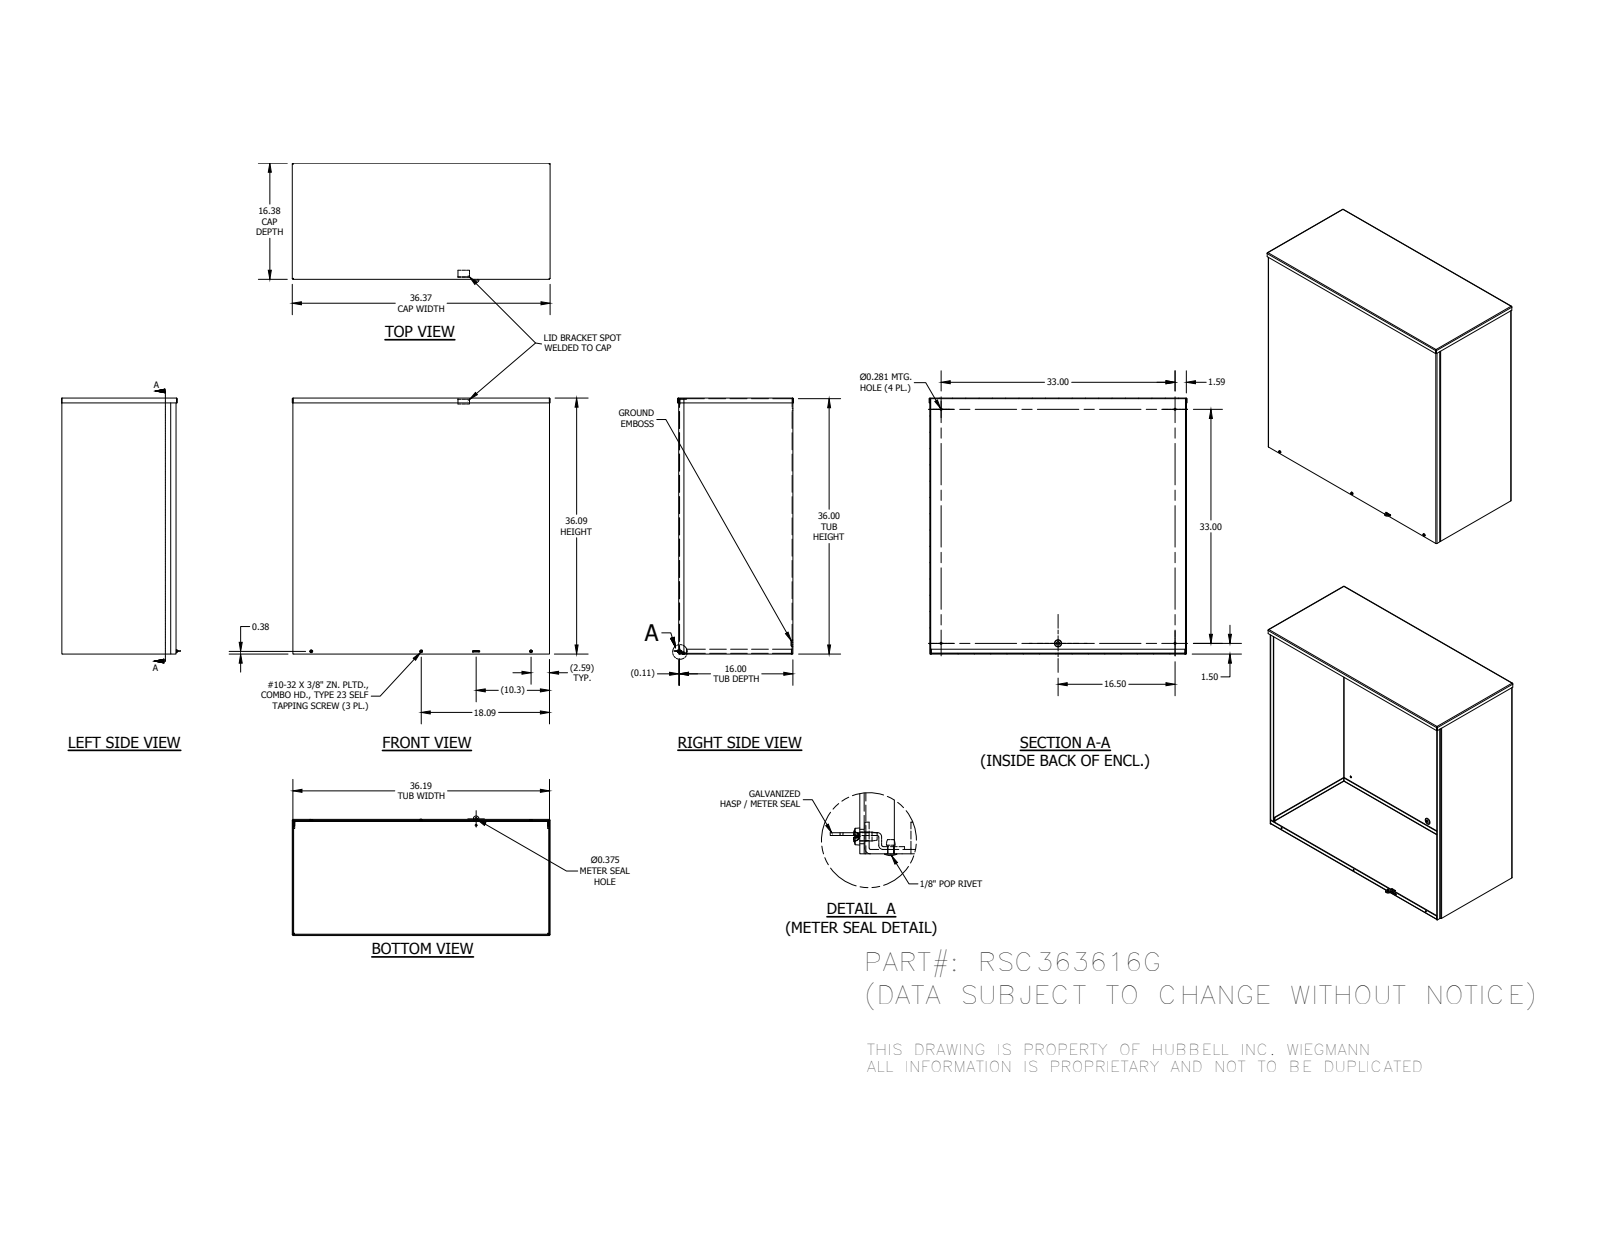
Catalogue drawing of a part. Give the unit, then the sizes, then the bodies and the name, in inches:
Units: inches
Overall size (bounding box): 36.375 × 36.134 × 16.844
Round holes (diameter × count): ⌀0.313 ×6, ⌀0.171 ×4, ⌀0.281 ×4, ⌀0.125 ×1, ⌀0.136 ×1, ⌀0.375 ×1
Round bosses / shafts (diameter × count): ⌀0.19 ×3, ⌀0.262 ×1, ⌀0.125 ×1
Partial cylindrical surfaces — rounded edges, fillets, slot ends (radius × count): R0.031 ×19, R0.125 ×16, R0.093 ×2, R0.105 ×1, R0.4 ×1
Main face-to-face distances: 0.094, 16.016, 36.094, 36, 16.109, 15.922, 36.187, 35.906, 0.149, 35.944
Hole centre spacings: 15.5, 32.02, 38.507, 16.538, 33, 1.506, 15.541, 31
Volume: 476.3 in³ · Surface area: 10 230 in²
Bodies: 11 solids, 367 faces (226 planar, 64 cylindrical, 77 other)
Part name (STEP PRODUCT): RSC363616GBKPA; RSC3616GEWPA; RSC3636GLFA; RSC3616GCPA (+5 more)
STEP written by: Autodesk Inventor 2014 (AUTOMOTIVE_DESIGN)
